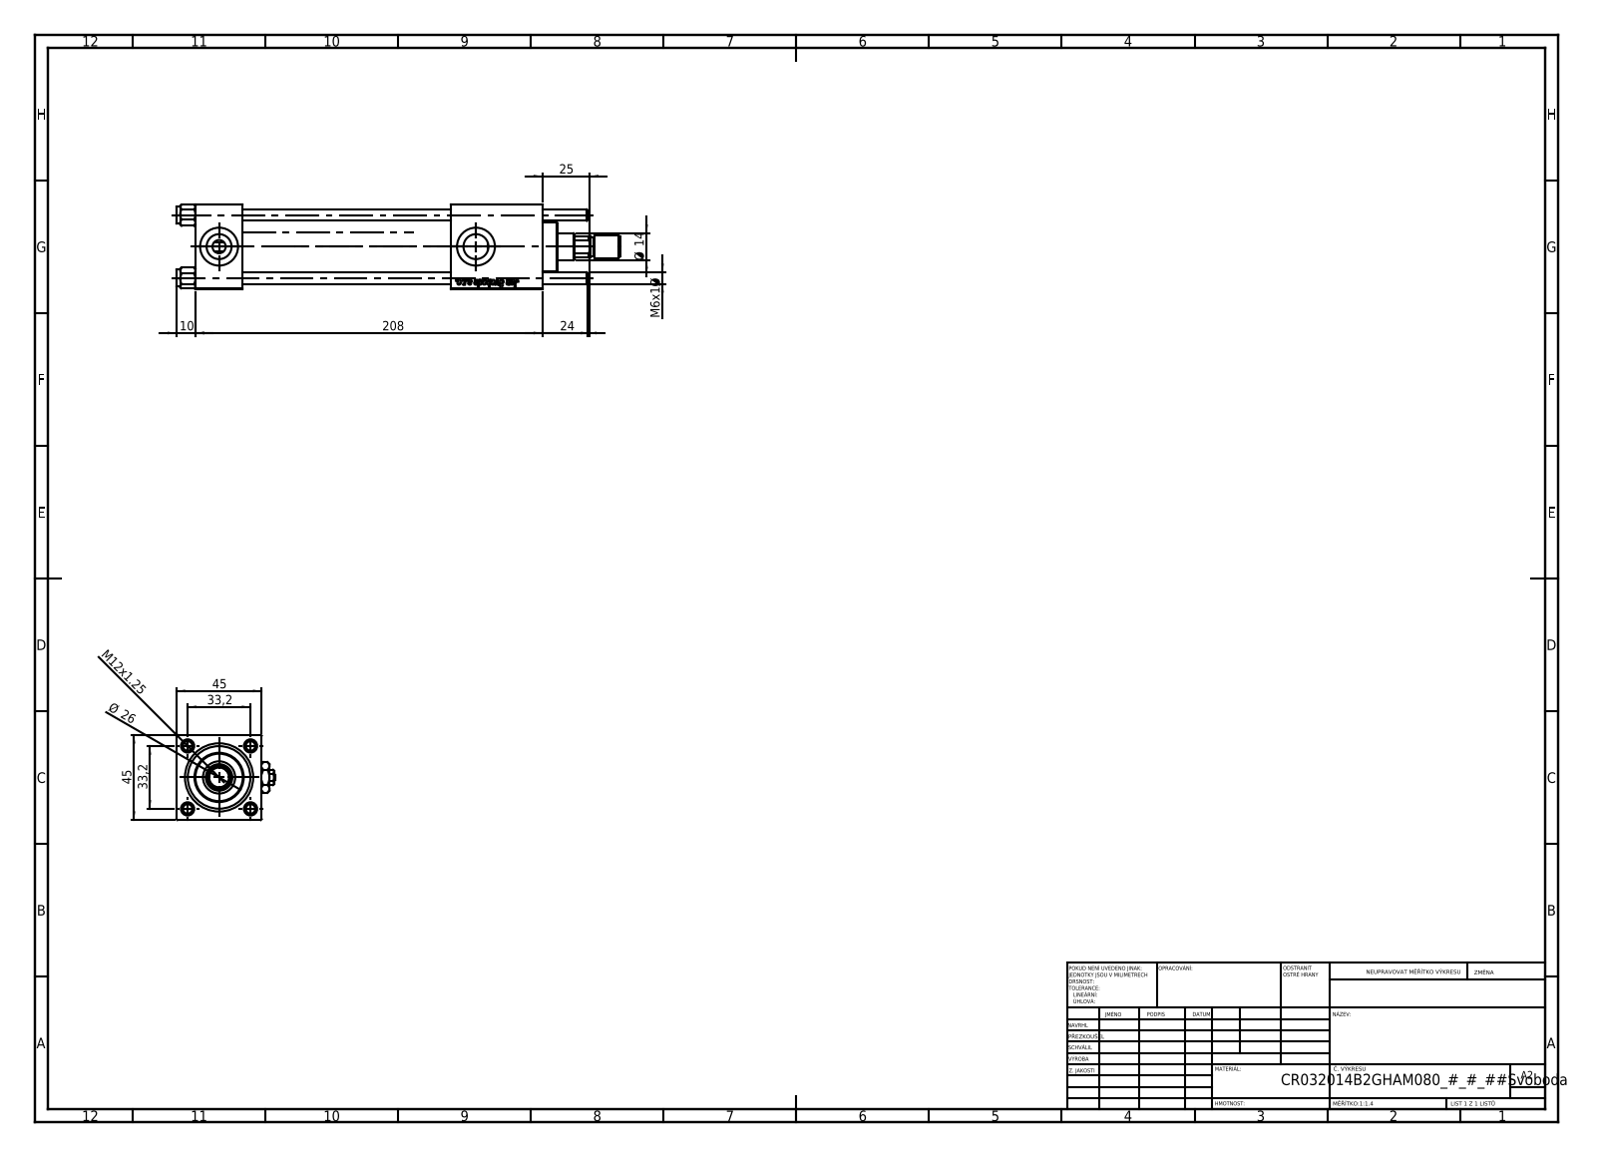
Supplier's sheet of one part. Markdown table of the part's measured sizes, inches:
| quantity | value |
| --- | --- |
| part name | ROD_END_AH; V215CR_B_TYCINKA; V215CR_B-1; NUT_M5_B (+3 more) |
| STEP written by | SolidWorks 2019 (CONFIG_CONTROL_DESIGN) |
| units | inches |
| bodies | 13 solids, 1222 faces (458 planar, 88 cylindrical, 676 other) |
| overall size | 9.213 × 2.047 × 1.772 |
| volume | 14.34 in³ |
| surface area | 147 in² |
| round holes (diameter × count) | 0.236 × 4, 0.276 × 2, 0.518 × 2, 0.787 × 2, 0.256 × 1, 0.551 × 1, 0.669 × 1, 0.945 × 1, 1.26 × 1, 1.299 × 1 |
| round bosses / shafts (diameter × count) | 0.354 × 4, 1.496 × 1, 1.024 × 1, 0.472 × 1, 0.394 × 1 |
| partial cylindrical surfaces (radius × count) | 0.256 × 1 |
| main face-to-face distances | 1.772, 0.984, 7.205, 6.22, 5.315, 4.331, 1.89, 6.075, 5.091, 0.76 |
| hole center spacings | 0.924, 1.307, 1.848, 5.335 |
